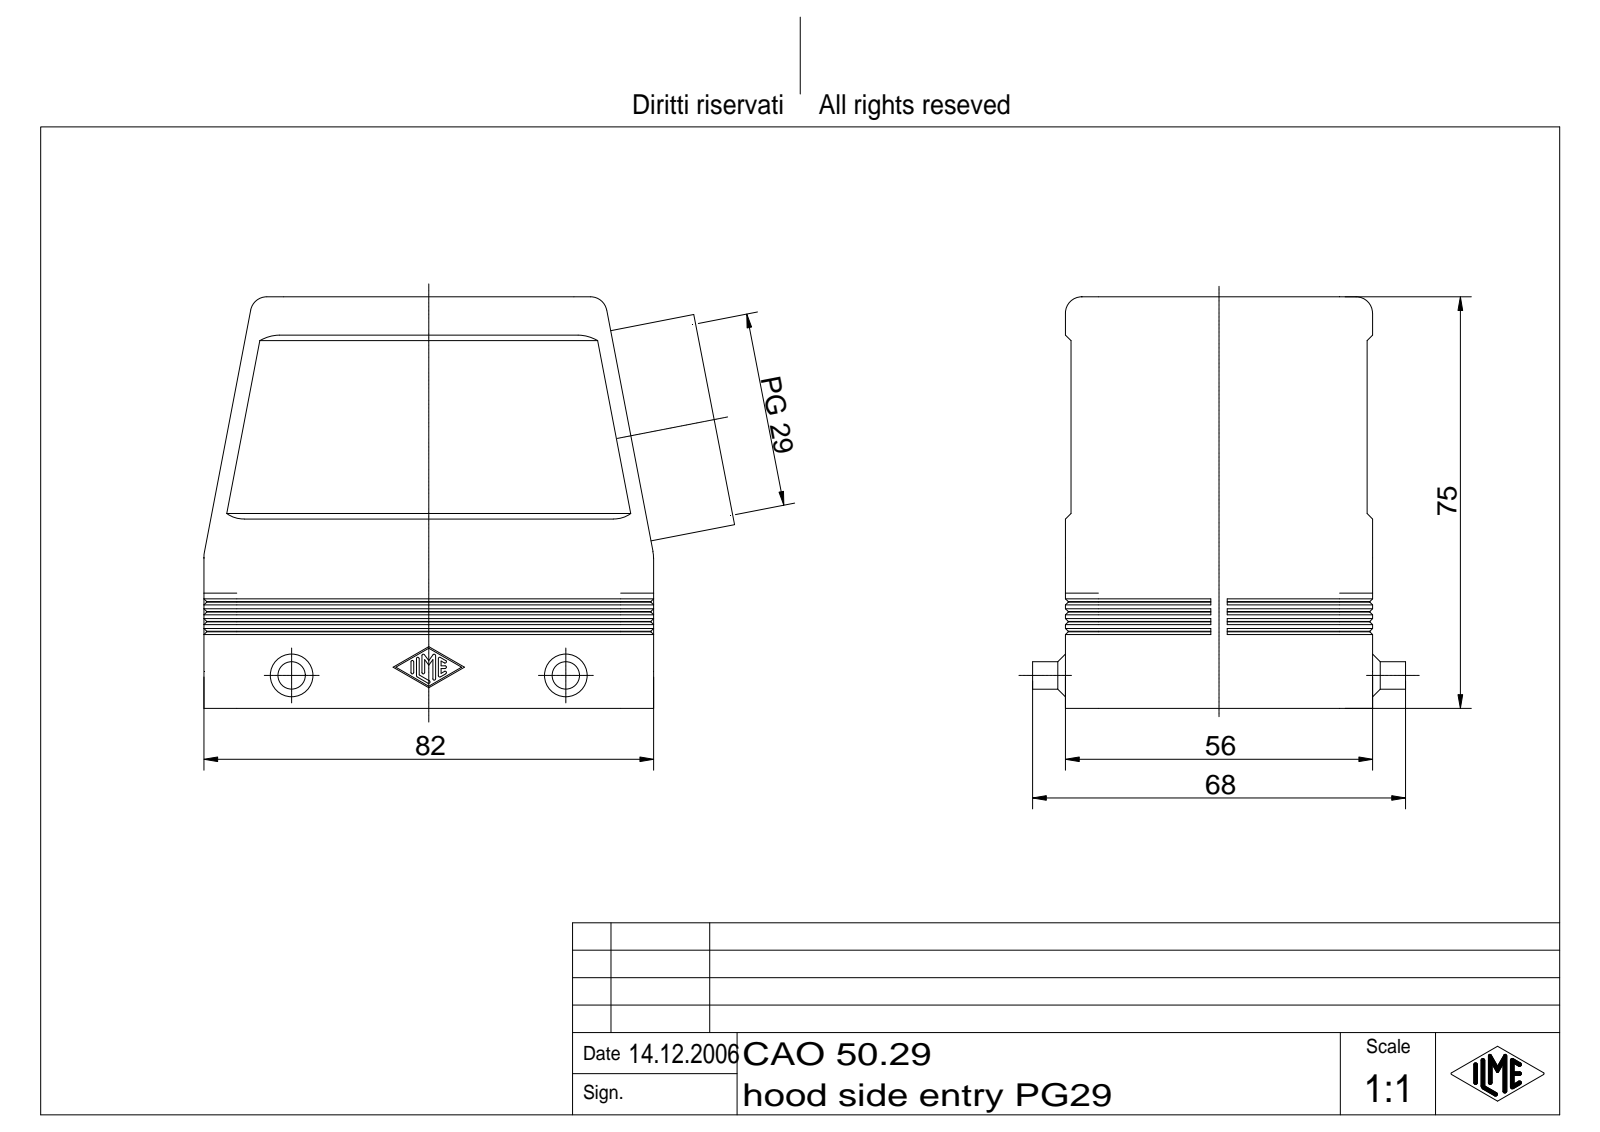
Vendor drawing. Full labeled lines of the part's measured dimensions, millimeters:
Part name (STEP PRODUCT): CAO 50.29
STEP written by: Autodesk Inventor 7 (AUTOMOTIVE_DESIGN)
Units: millimetres
Bodies: 1 solid, 461 faces (168 planar, 138 cylindrical, 155 other)
Overall size (bounding box): 96.76 × 75 × 68
Volume: 76 518 mm³ · Surface area: 48 851 mm²
Round holes (diameter × count): ⌀2.46 ×4, ⌀3.5 ×4, ⌀33.48 ×1, ⌀35.48 ×1
Round bosses / shafts (diameter × count): ⌀5 ×2, ⌀39 ×1
Partial cylindrical surfaces — rounded edges, fillets, slot ends (radius × count): R0.25 ×14, R6 ×10, R2 ×8, R3 ×8, R5.5 ×2
Main face-to-face distances: 3, 53, 50, 56, 2, 1, 52, 55, 11.25, 70.75
Hole centre spacings: 16, 66, 67.91
